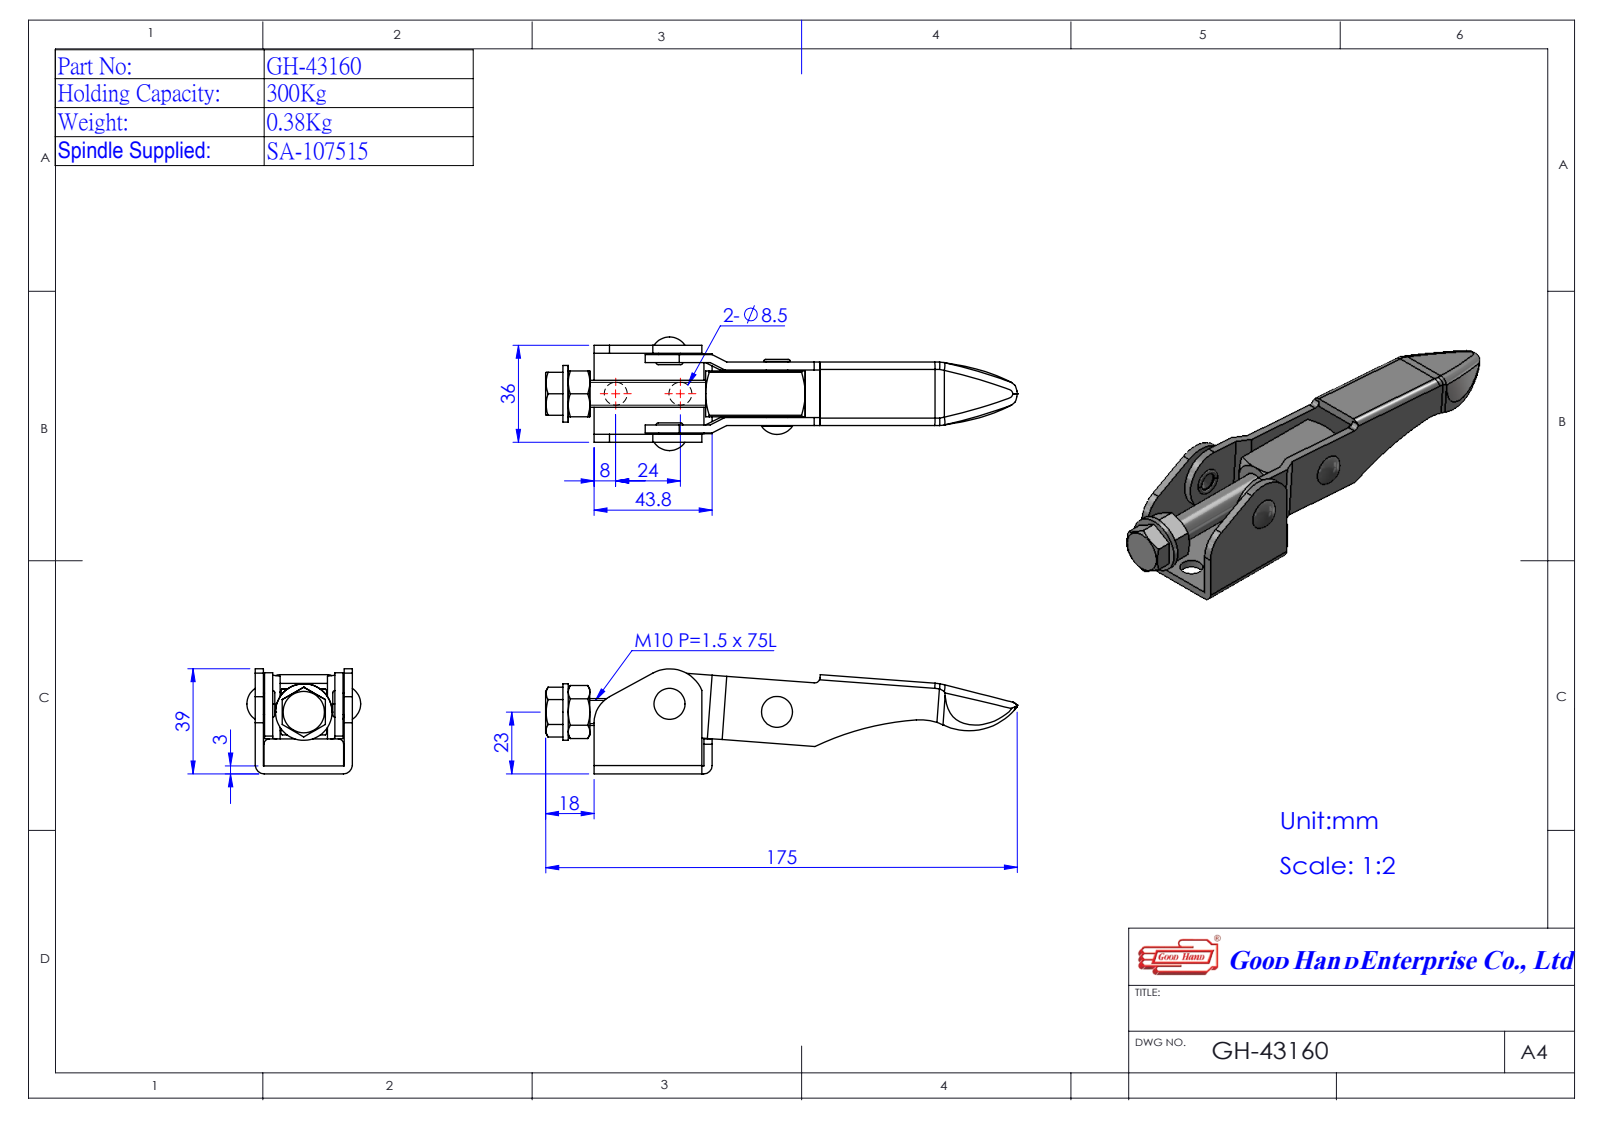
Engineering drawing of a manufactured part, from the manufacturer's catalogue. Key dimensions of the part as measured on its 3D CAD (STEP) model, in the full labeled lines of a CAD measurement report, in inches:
Part name (STEP PRODUCT): Group1^GH-43160(簡化); Group4^GH-43160(簡化); GH-43160(簡化); Group2^GH-43160(簡化) (+1 more)
STEP written by: SolidWorks 2016 (AUTOMOTIVE_DESIGN)
Units: inches
Bodies: 9 solids, 216 faces (85 planar, 66 cylindrical, 65 other)
Overall size (bounding box): 6.894 × 1.661 × 1.535
Volume: 3.047 in³ · Surface area: 50.68 in²
Round holes (diameter × count): ⌀0.335 ×4, ⌀0.236 ×2, ⌀0.394 ×1
Round bosses / shafts (diameter × count): ⌀0.827 ×1, ⌀0.394 ×1, ⌀0.315 ×1
Partial cylindrical surfaces — rounded edges, fillets, slot ends (radius × count): R0.079 ×3, R0.118 ×2, R0.13 ×2, R0.138 ×2, R0.787 ×2, R0.122 ×1, R0.433 ×1, R0.463 ×1
Main face-to-face distances: 0.118, 1.055, 0.244, 0.811, 0.126, 0.937, 1.173, 0.362, 1.299, 0.136
Hole centre spacings: 0.945, 1.575
